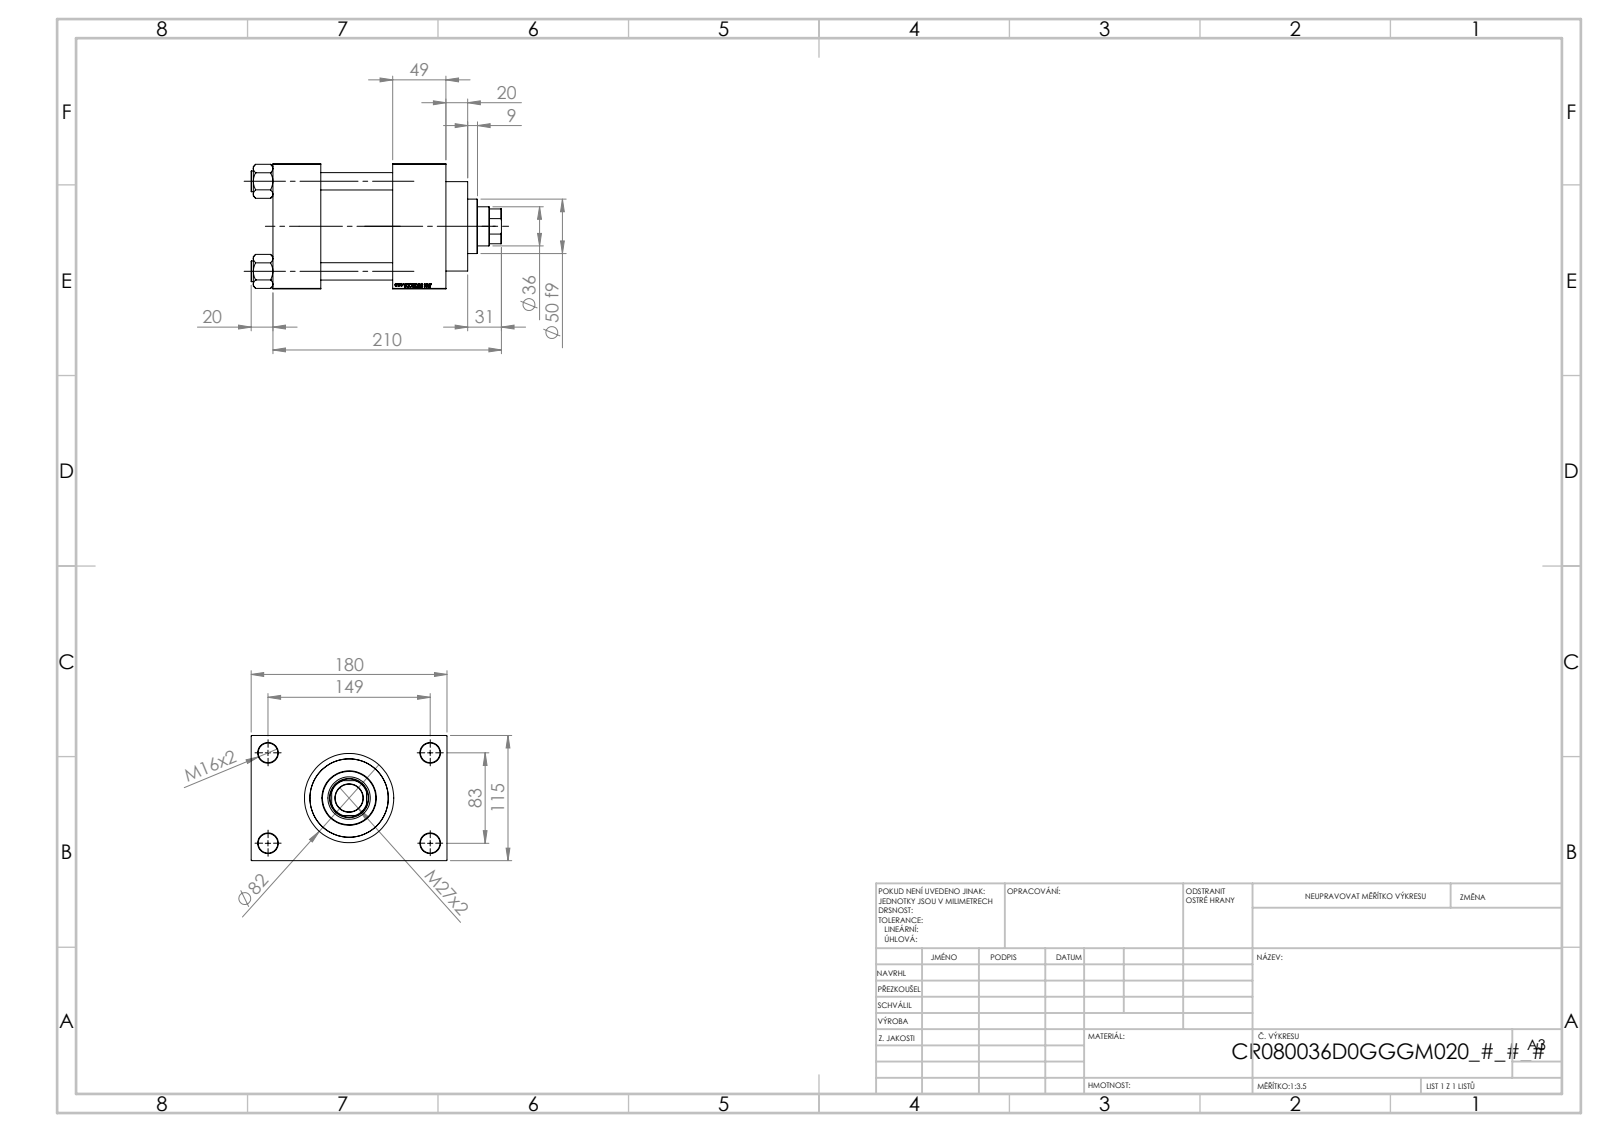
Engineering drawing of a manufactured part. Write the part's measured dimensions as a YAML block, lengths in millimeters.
part_name: "NUT_M5_D; V215CR_D_Body; V215CR_D_TYCINKA; V215CR_VCP_D (+1 more)"
step_written_by: "SolidWorks 2019 (CONFIG_CONTROL_DESIGN)"
units: millimeters
bodies: {solids: 11, faces: 1152, planar: 545, cylindrical: 89, other: 518}
overall_size: [230, 180, 115]
volume: 1997000
surface_area: 293903
round_holes:
  - {diameter: 16, count: 4}
  - {diameter: 18, count: 4}
  - {diameter: 7, count: 2}
  - {diameter: 26.44, count: 2}
  - {diameter: 35, count: 2}
  - {diameter: 25.5, count: 1}
  - {diameter: 36, count: 1}
  - {diameter: 39, count: 1}
  - {diameter: 61, count: 1}
  - {diameter: 72, count: 1}
  - {diameter: 80, count: 1}
round_bosses_or_shafts:
  - {diameter: 19, count: 4}
  - {diameter: 86, count: 1}
  - {diameter: 82, count: 1}
  - {diameter: 50, count: 1}
partial_cylinders:
  - {radius: 17.5, count: 1}
face_to_face_distances: [115, 66, 110, 49, 44, 159, 32.5, 147.5, 20, 69]
hole_center_spacings: [33.15, 58.48, 82.7, 85.28, 89.24, 115.85, 142.43, 83]
